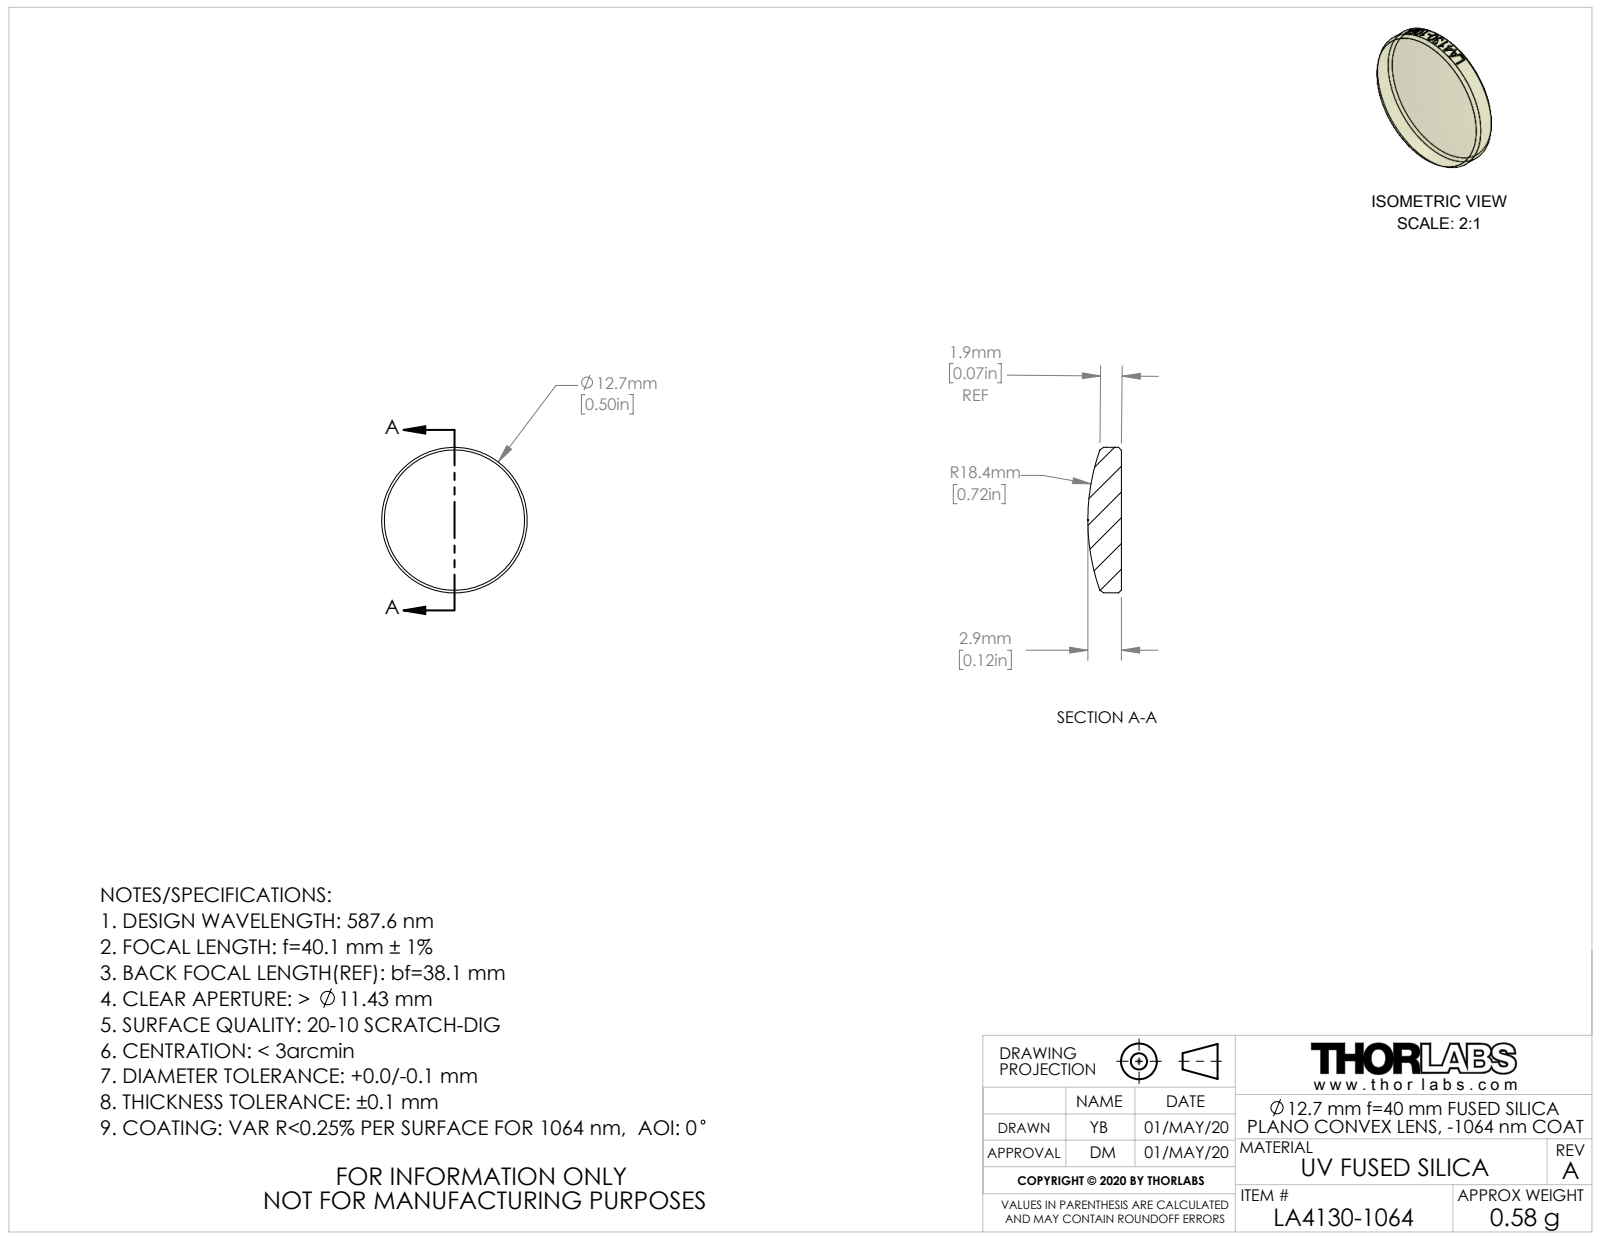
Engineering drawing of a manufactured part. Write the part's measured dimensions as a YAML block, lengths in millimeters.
part_name: "CTN015542-E0W"
step_written_by: "SolidWorks 2018 (AUTOMOTIVE_DESIGN)"
units: millimeters
bodies: {solids: 1, faces: 27, planar: 1, cylindrical: 20, other: 6}
overall_size: [12.7, 12.7, 2.93]
volume: 298
surface_area: 320
round_bosses_or_shafts:
  - {diameter: 12.7, count: 1}
